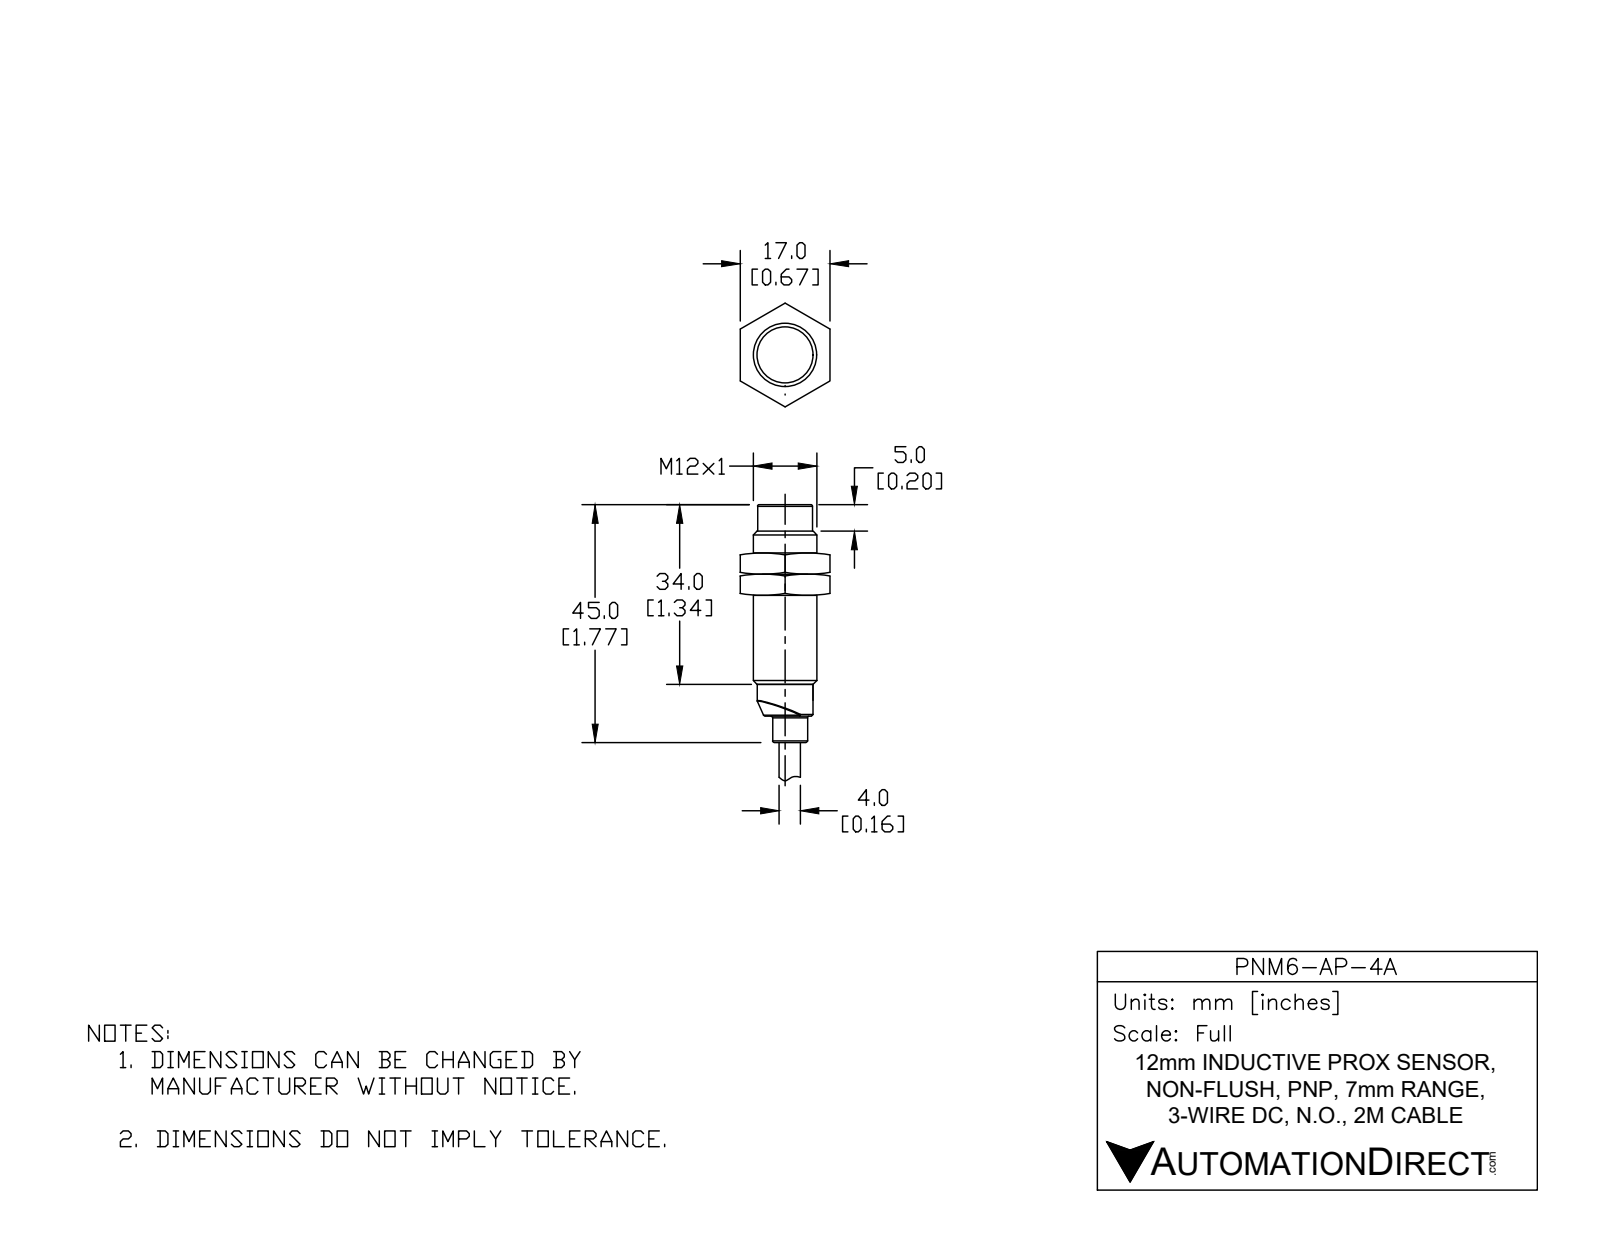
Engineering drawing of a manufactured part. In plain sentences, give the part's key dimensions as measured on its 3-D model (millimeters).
The part is named "PNM6-AP-4A". Its 3-D file was written by "SolidWorks 2017 (AUTOMOTIVE_DESIGN)". It is 1 solid with 59 faces: 13 planar, 23 cylindrical and 23 other. Overall it measures 95.8 by 12 by 12 millimeters. Its volume is 5 130 cubic millimeters and its surface area 2 606 square millimeters. Round holes: 1 of diameter 4.1. Round bosses or shafts: 3 of diameter 1.2, 1 of diameter 12, 1 of diameter 10.6, 1 of diameter 10.5, 1 of diameter 6.6, 1 of diameter 4. Partial cylindrical surfaces (rounded edges, fillets, slot ends): 1 of radius 0.6, 1 of radius 2. The main face-to-face distances are 40, 45, 5, 95.8, 55.8, 50.8, 37, 3, 8, 58.8.
